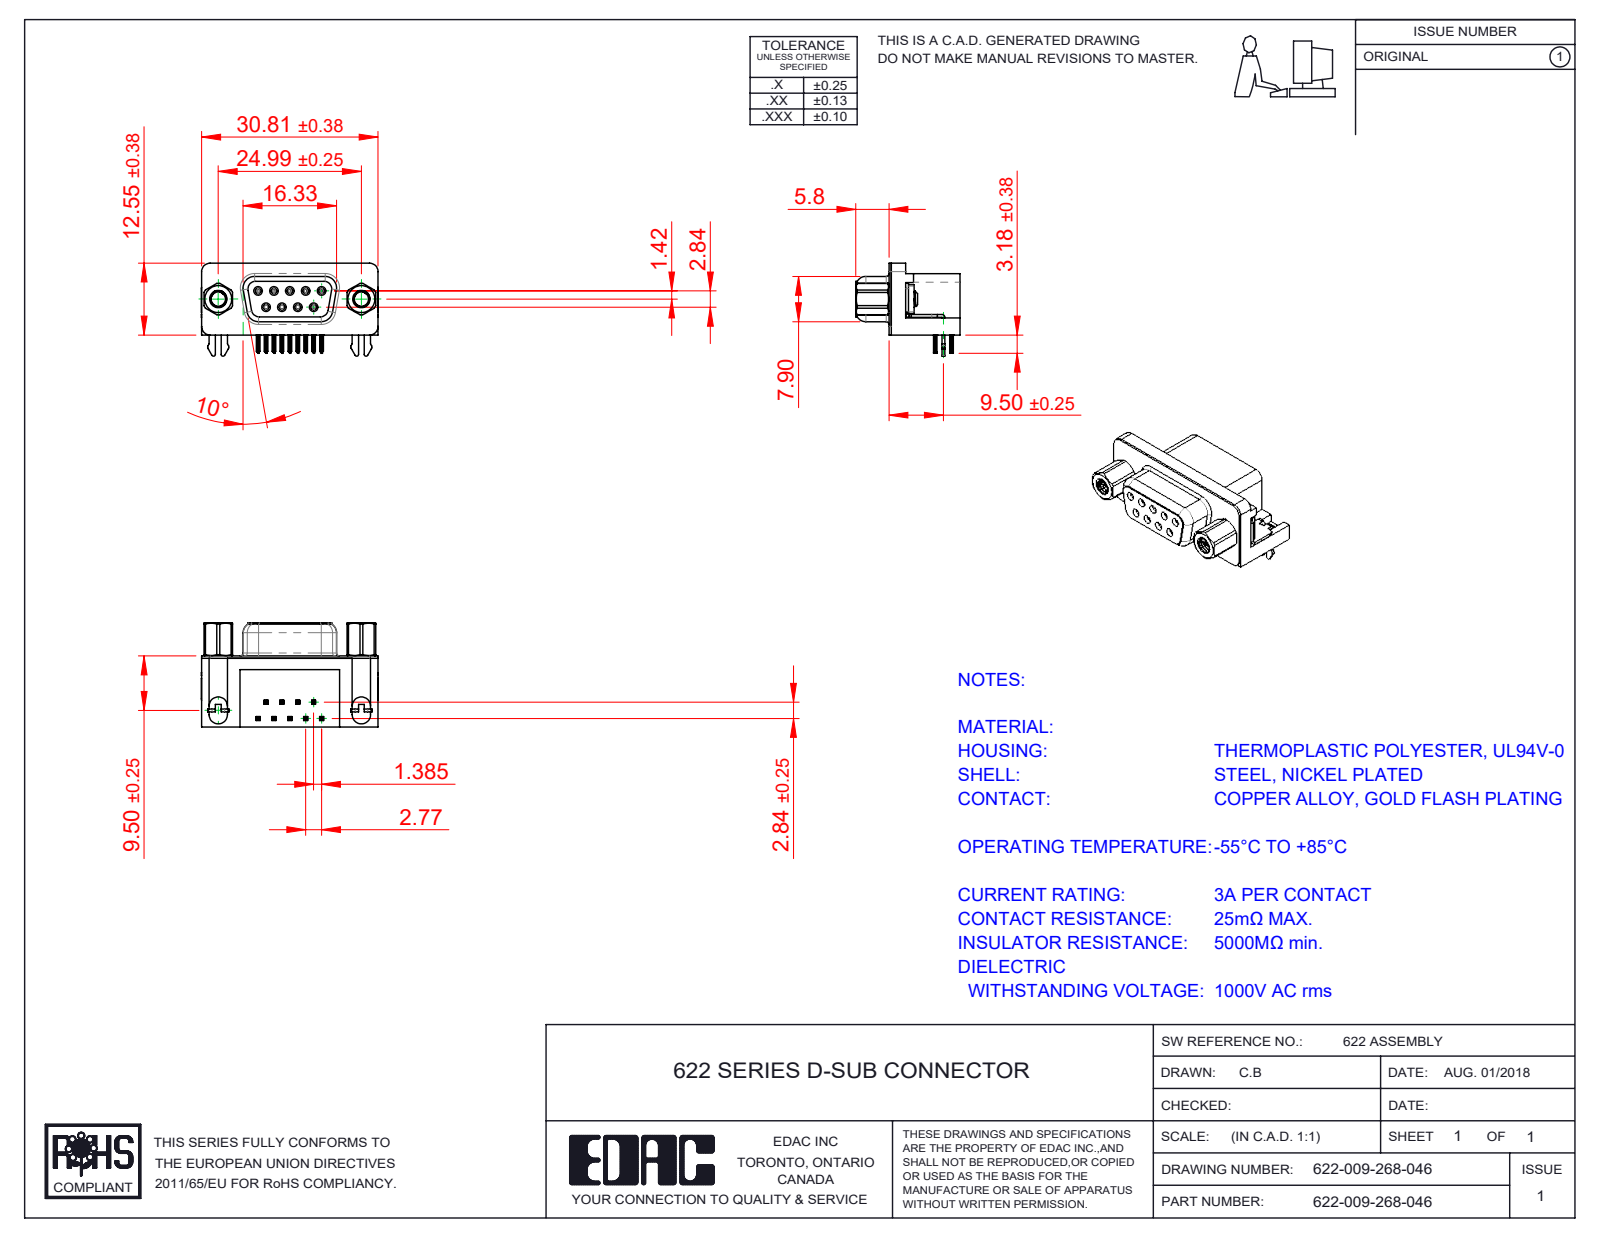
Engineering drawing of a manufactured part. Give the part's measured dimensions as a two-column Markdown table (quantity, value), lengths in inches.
| quantity | value |
| --- | --- |
| part name | 622 Housing_9 Socket; 622-009-268-046; 622 M3 Threaded Rivet; 622 Contact Top (+3 more) |
| STEP written by | SolidWorks 2016 (CONFIG_CONTROL_DESIGN) |
| units | inches |
| bodies | 15 solids, 1692 faces (726 planar, 426 cylindrical, 540 other) |
| overall size | 1.216 × 0.717 × 0.64 |
| volume | 0.228 in³ |
| surface area | 7.984 in² |
| round holes (diameter × count) | 0.031 × 9, 0.035 × 9, 0.079 × 2, 0.098 × 2, 0.157 × 2, 0.189 × 2, 0.197 × 2 |
| round bosses / shafts (diameter × count) | 0.047 × 9, 0.193 × 2, 0.187 × 2, 0.154 × 2, 0.118 × 2 |
| partial cylindrical surfaces (radius × count) | 0.004 × 72, 0.006 × 36, 0.014 × 18, 0.039 × 18, 0.01 × 12, 0.013 × 9, 0.053 × 8, 0.063 × 8 |
| main face-to-face distances | 0.016, 0.472, 0.488, 0.014, 0.114, 0.098, 0.244, 0.407, 0.374, 0.228 |
| hole center spacings | 0.124, 0.109, 0.218, 0.198, 0.198, 0.327, 0.294, 0.295 |
